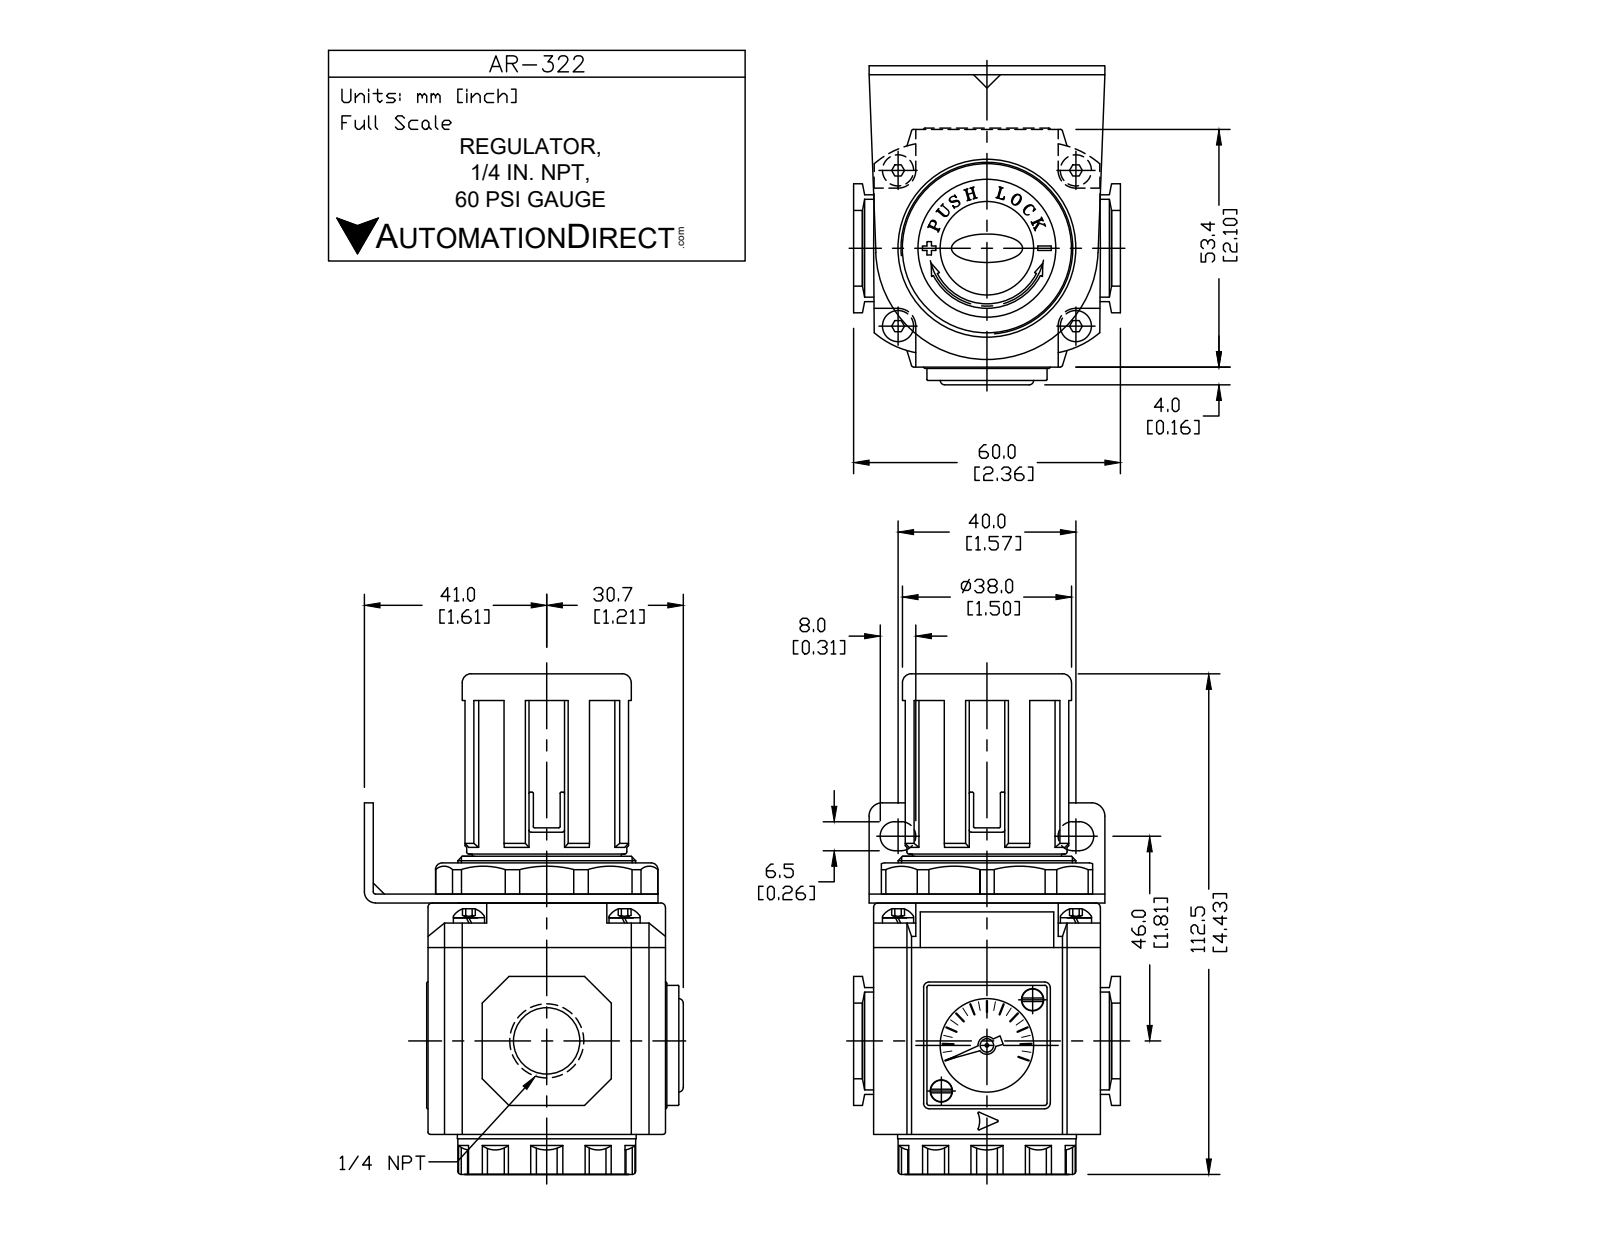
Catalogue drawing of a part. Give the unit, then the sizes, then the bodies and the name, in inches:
Units: inches
Overall size (bounding box): 4.429 × 2.783 × 2.362
Round holes (diameter × count): ⌀0.118 ×6, ⌀0.079 ×1, ⌀0.438 ×1, ⌀0.827 ×1, ⌀1.181 ×1, ⌀1.26 ×1
Round bosses / shafts (diameter × count): ⌀0.217 ×4, ⌀0.106 ×2, ⌀1.575 ×1, ⌀1.543 ×1, ⌀1.496 ×1, ⌀1.319 ×1, ⌀0.806 ×1, ⌀0.157 ×1
Partial cylindrical surfaces — rounded edges, fillets, slot ends (radius × count): R0.039 ×12, R0.047 ×10, R0.128 ×6, R0.157 ×5, R0.012 ×4, R0.783 ×4, R0.008 ×3, R0.079 ×1
Main face-to-face distances: 0.079, 2.047, 2.126, 2.102, 0.039, 0.354, 2.402, 2.185, 2.008, 2.063
Hole centre spacings: 1.046, 0.571, 1.378, 1.575, 2.093, 1.141
Volume: 12.85 in³ · Surface area: 67.6 in²
Bodies: 14 solids, 501 faces (326 planar, 133 cylindrical, 42 other)
Part name (STEP PRODUCT): AR-322
STEP written by: SolidWorks 2015 (CONFIG_CONTROL_DESIGN)
